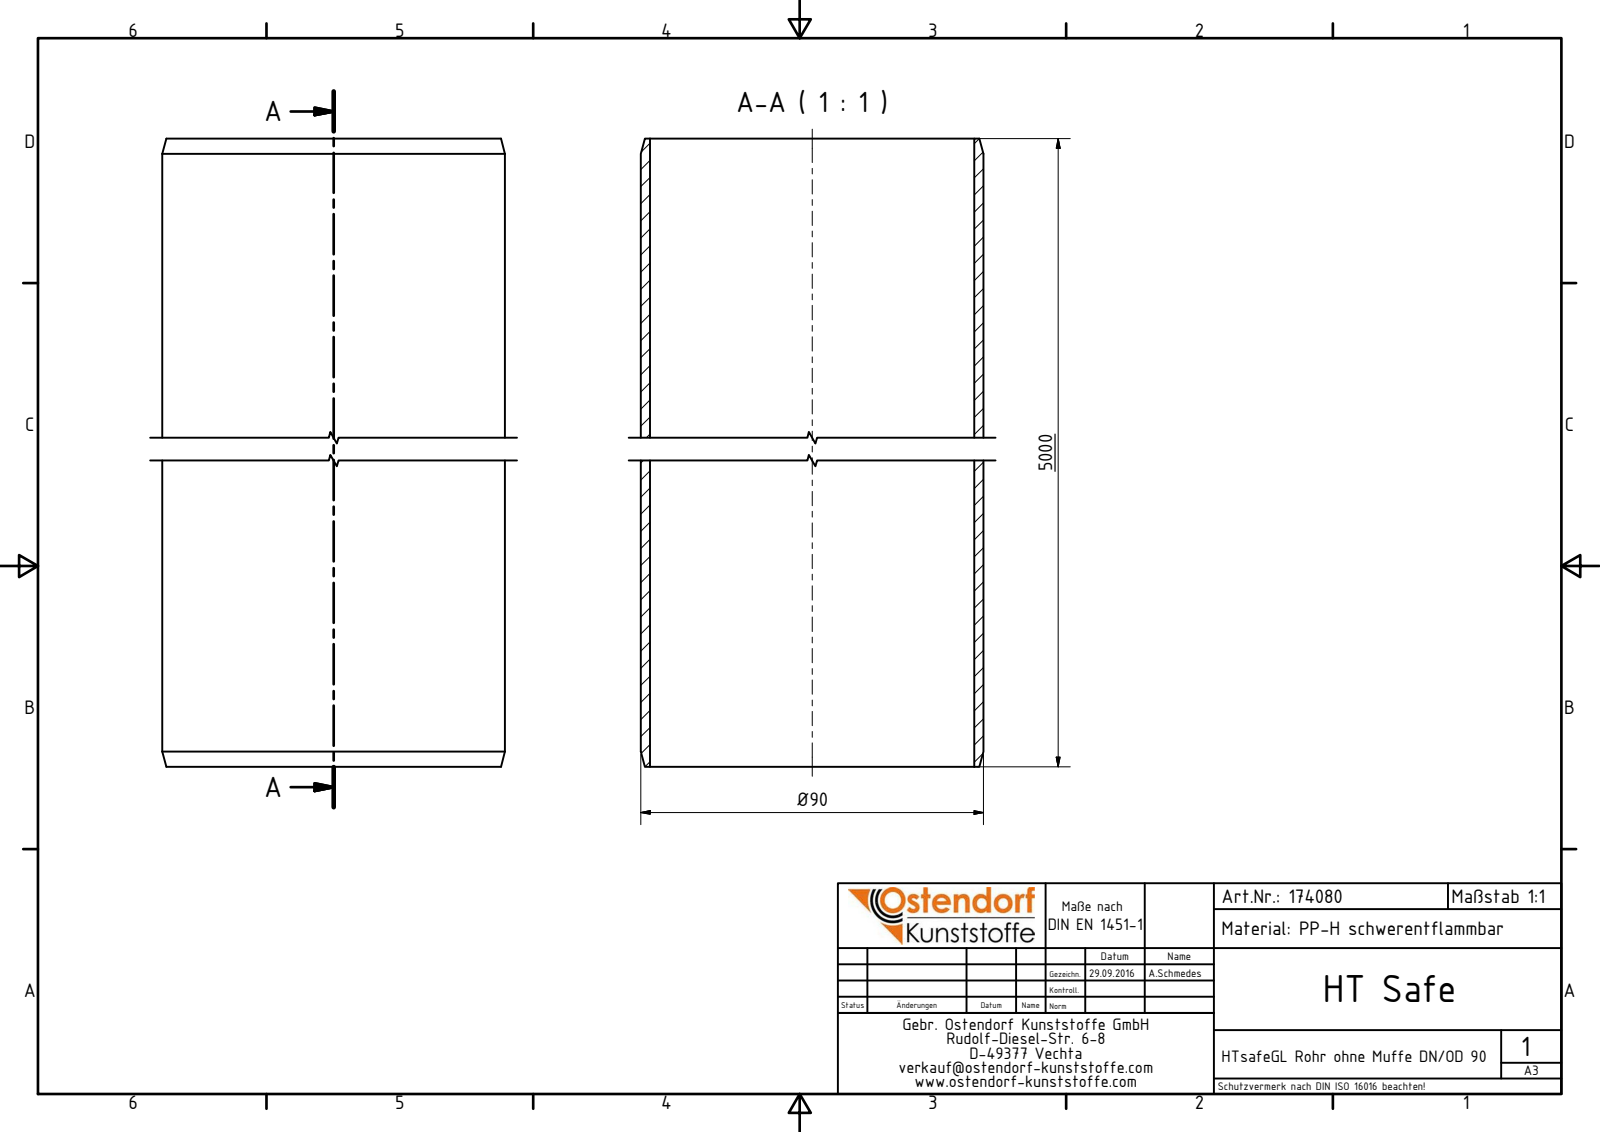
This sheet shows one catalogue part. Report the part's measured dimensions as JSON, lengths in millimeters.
{"part_name": "174080 HTsafeGL DN_OD 90x5000", "step_written_by": "Autodesk Inventor 2016 (AUTOMOTIVE_DESIGN)", "units": "millimeters", "bodies": {"solids": 1, "faces": 6, "planar": 2, "cylindrical": 2, "other": 2}, "overall_size": [5000, 90, 90], "volume_mm3": 3301000, "surface_area_mm2": 2753000, "round_holes": [[85.2, 1]], "round_bosses_or_shafts": [[90, 1]], "face_to_face_distances": [5000]}
